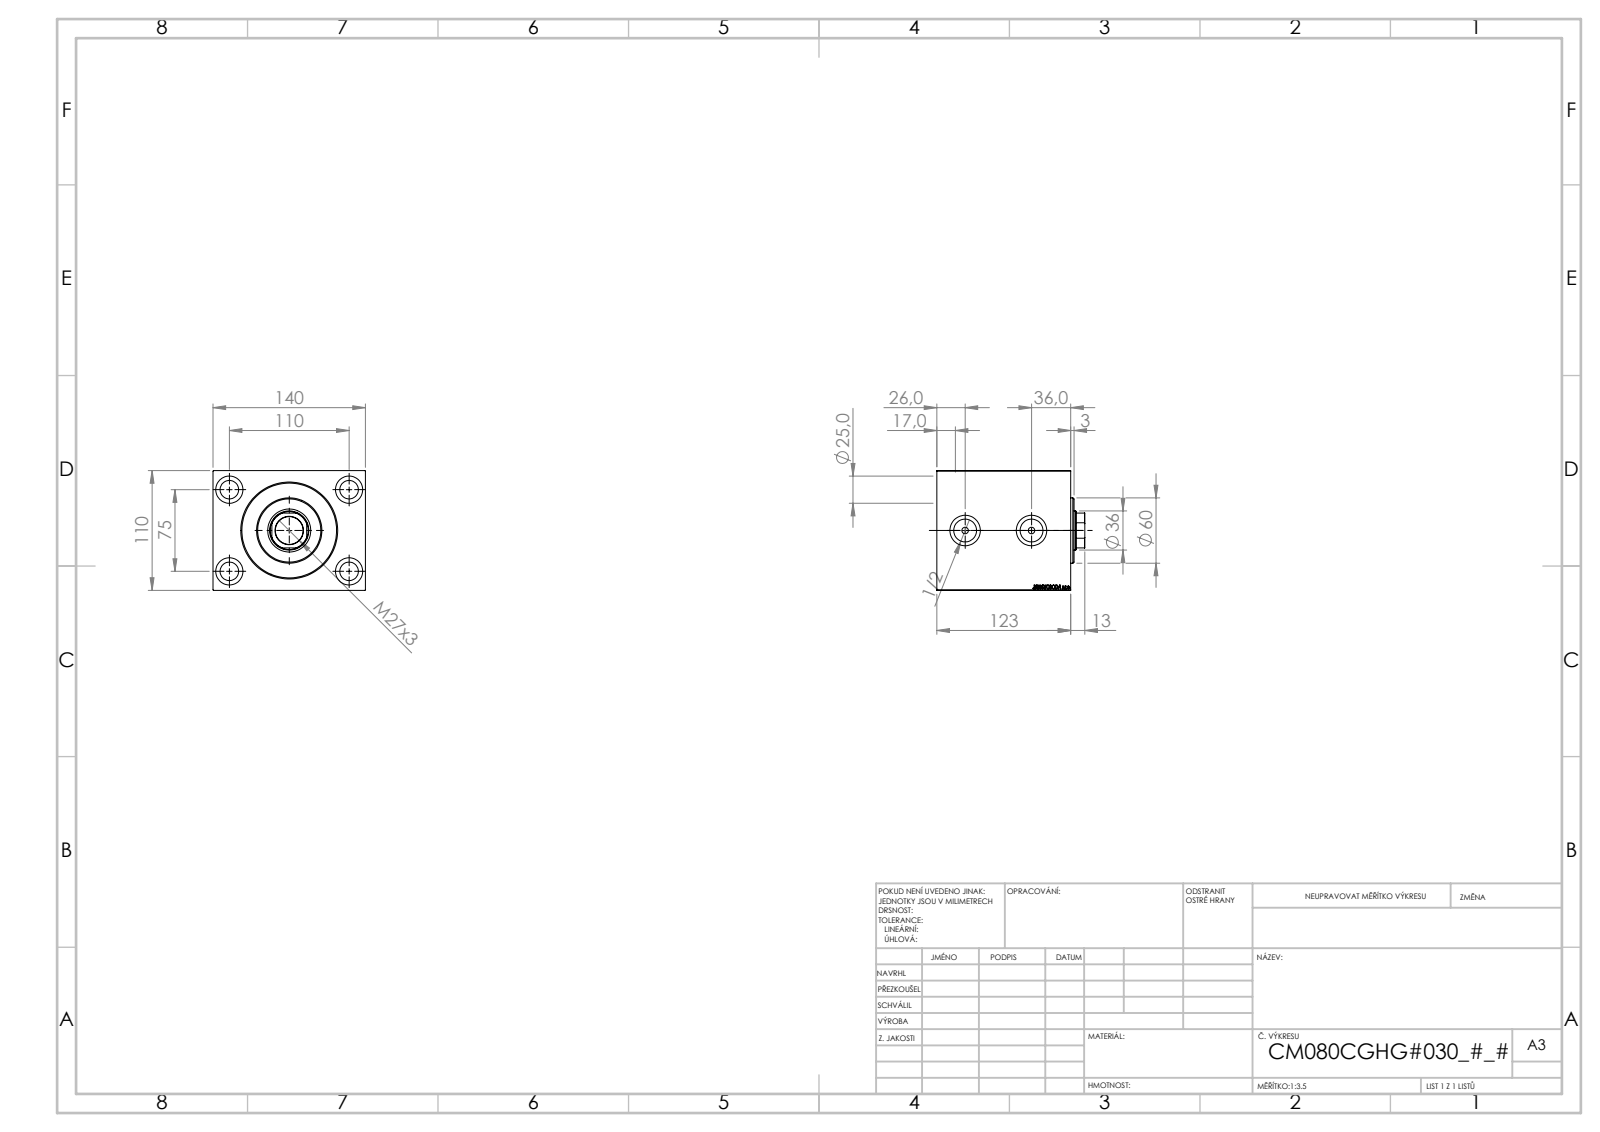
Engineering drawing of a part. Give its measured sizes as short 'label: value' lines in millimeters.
name: V450CM_C_Body; V450CM_C_VCP; V450CM_VC_B
written by: SolidWorks 2019 (CONFIG_CONTROL_DESIGN)
unit: mm
bodies: 3 solids, 866 faces (410 planar, 62 cylindrical, 394 other)
size: 140 × 137 × 110
volume: 1 616 000 mm³; area: 178 125 mm²
holes: 4× ⌀17, 4× ⌀25, 2× ⌀6, 2× ⌀20.96, 2× ⌀28, 1× ⌀25.5, 1× ⌀36, 1× ⌀39.5, 1× ⌀80, 1× ⌀82, 1× ⌀87
bosses: 1× ⌀60
rounds: 1× R17.5
face distances: 110, 140, 123, 63.25, 59.75, 10, 53.25, 113, 40, 30
hole spacings: 66.57, 75, 110, 133.14, 61
